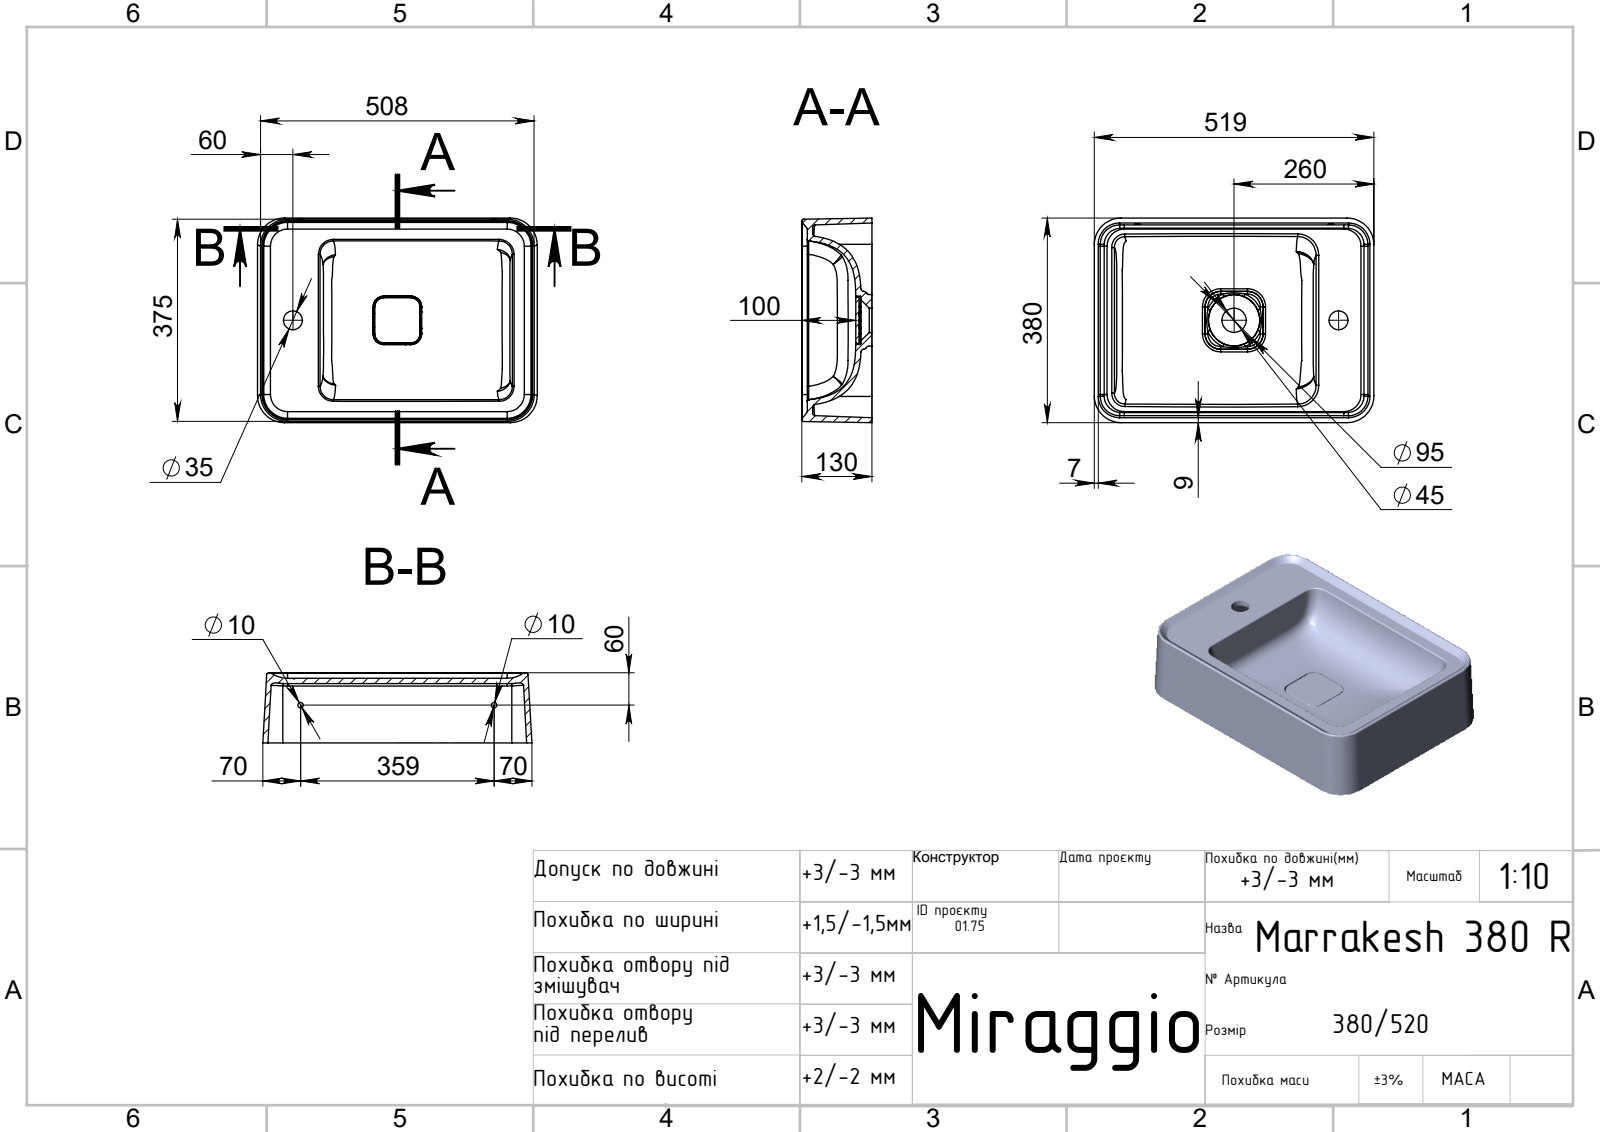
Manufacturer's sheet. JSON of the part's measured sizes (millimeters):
{"part_name": "Marrakesh 380 R", "step_written_by": "SolidWorks 2020 (AUTOMOTIVE_DESIGN)", "units": "millimeters", "bodies": {"solids": 2, "faces": 254, "planar": 40, "cylindrical": 44, "other": 170}, "overall_size": [519.12, 379.65, 130], "volume_mm3": 4306000, "surface_area_mm2": 923978, "round_holes": [[10, 2], [35, 1], [45, 1]], "partial_cylinders_radius": [[3, 7], [5, 7], [1.8, 5], [2, 5], [1, 4], [50, 4], [45, 1]], "face_to_face_distances": [10, 110, 120, 90, 24, 86, 96, 30, 6, 80], "hole_center_spacings": [193.88, 359.12]}
